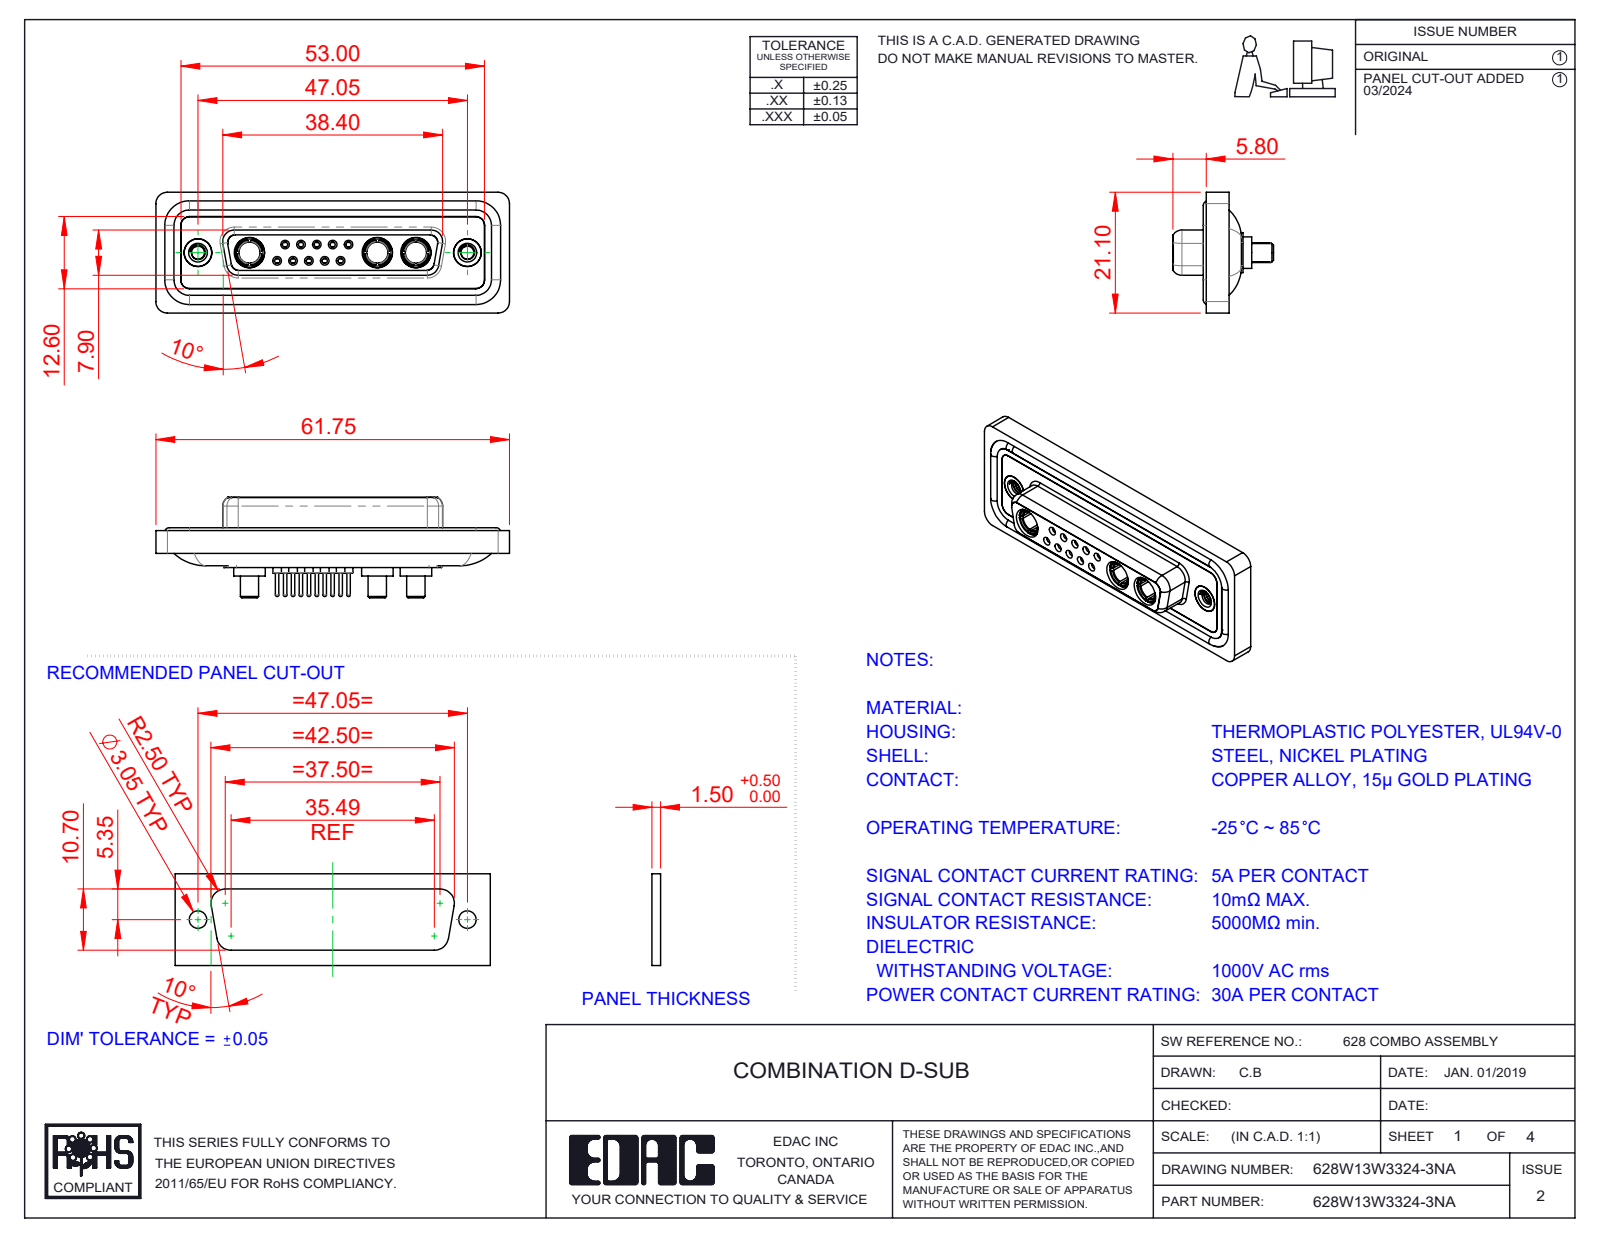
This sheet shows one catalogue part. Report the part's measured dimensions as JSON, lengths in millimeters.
{"part_name": "628Combo Shell Rear_25 Contacts; 628Combo Contact Row 1_24; 628W13W3324-3NA; 628Combo Contact Row 2_24 (+5 more)", "step_written_by": "SolidWorks 2023 (CONFIG_CONTROL_DESIGN)", "units": "millimeters", "bodies": {"solids": 23, "faces": 1156, "planar": 342, "cylindrical": 449, "other": 365}, "overall_size": [61.75, 21.1, 17.55], "volume_mm3": 8296, "surface_area_mm2": 13720, "round_holes": [[0.9, 10], [1.1, 10], [1.5, 10], [2, 10], [1.6, 5], [1.7, 5], [4.85, 5], [3.7, 3], [5.3, 3], [2.26, 2], [4, 2], [4.05, 2]], "round_bosses_or_shafts": [[2.2, 10], [0.6, 10], [1.6, 9], [5.5, 3], [5.2, 3], [4.96, 3], [4.75, 3], [3.75, 3]], "partial_cylinders_radius": [[1.5, 22], [2, 18], [1.35, 8], [1.6, 8], [0.25, 4], [0.5, 4], [0.6, 4], [0.65, 4]], "face_to_face_distances": [0.4, 1.8, 7.45, 5.65, 0.5, 6.6, 7.05, 1.6, 2.9, 1.1], "hole_center_spacings": [3.16, 2.77, 5.03, 5.04, 5.54, 8.31, 7.49, 2.76]}
